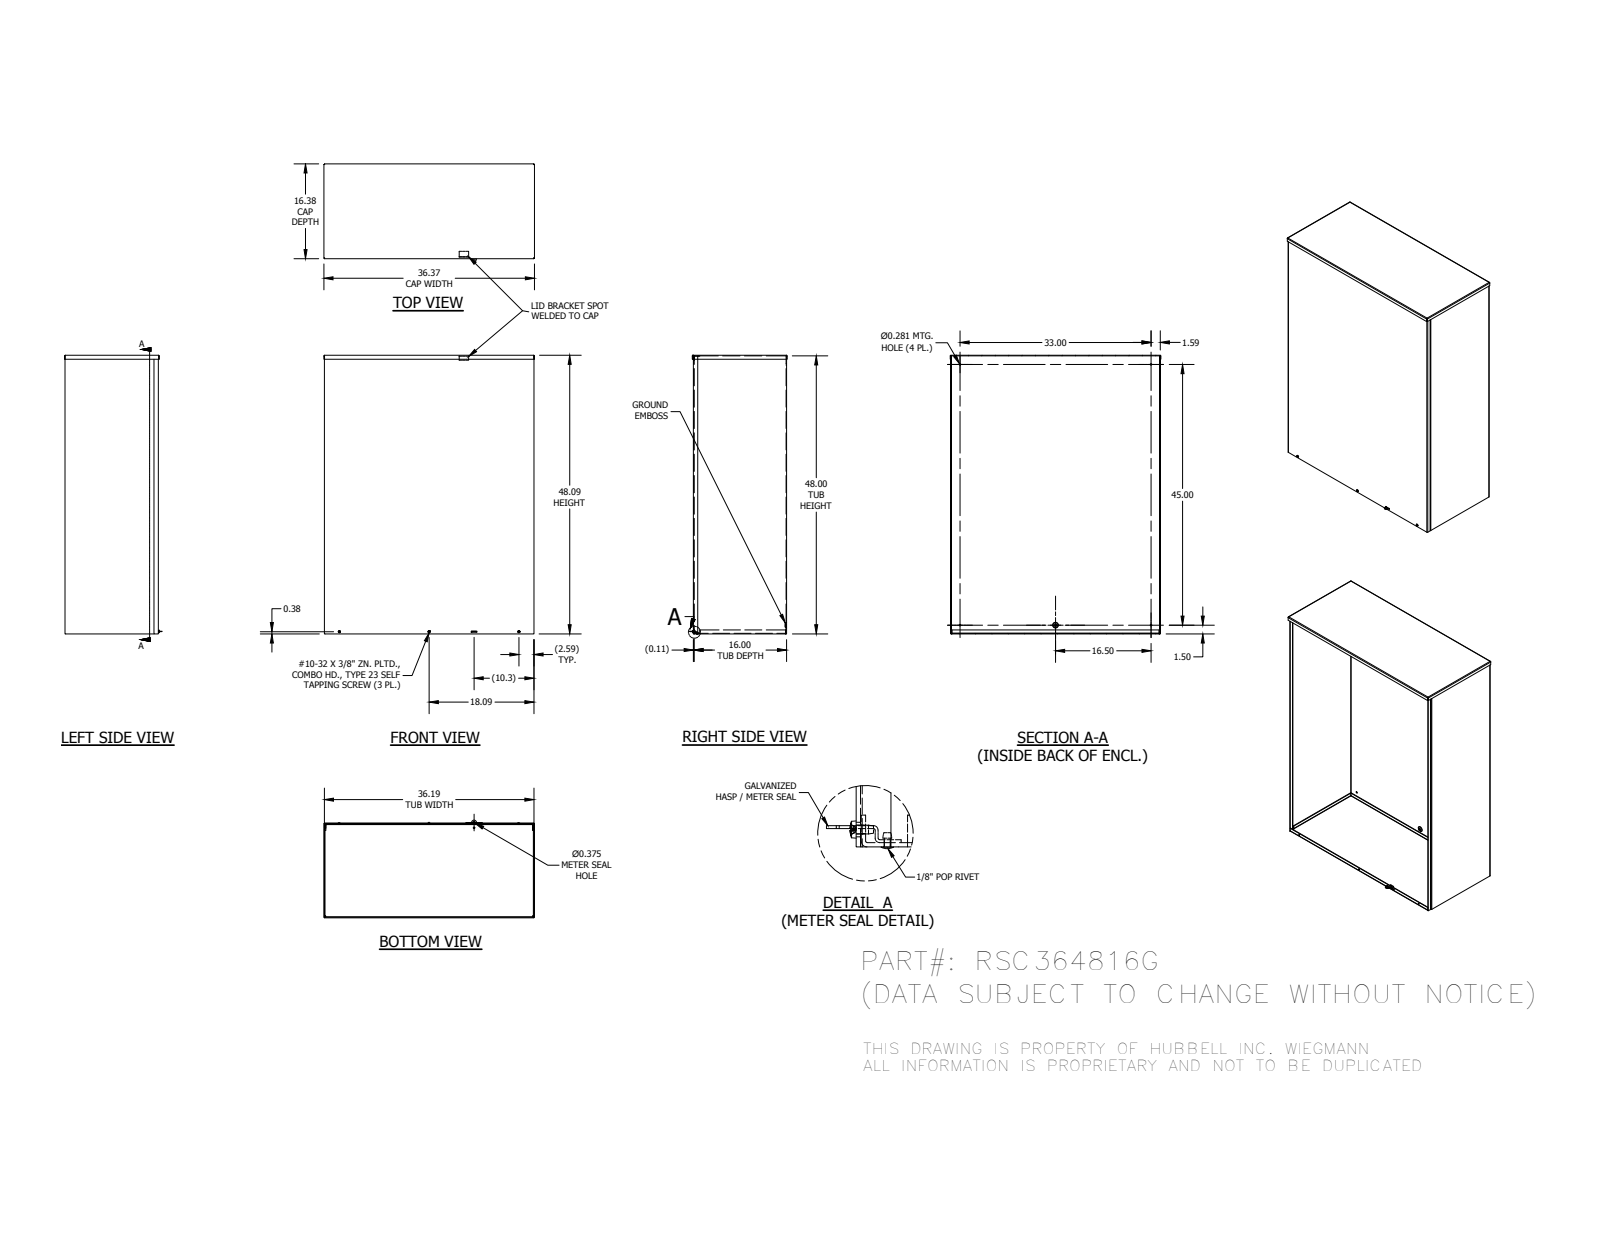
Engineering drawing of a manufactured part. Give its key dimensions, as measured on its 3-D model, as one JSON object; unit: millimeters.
{"part_name": "RSC364816GBKPA; RSC3616GEWPA; RSC3648GLFA; RSC3616GCPA (+5 more)", "step_written_by": "Autodesk Inventor 2014 (AUTOMOTIVE_DESIGN)", "units": "millimeters", "bodies": {"solids": 11, "faces": 367, "planar": 226, "cylindrical": 64, "other": 77}, "overall_size": [1222.6, 923.92, 427.84], "volume_mm3": 9748000, "surface_area_mm2": 8233000, "round_holes": [[7.94, 6], [4.34, 4], [7.14, 4], [3.17, 1], [3.45, 1], [9.52, 1]], "round_bosses_or_shafts": [[4.83, 3], [6.65, 1], [3.17, 1]], "partial_cylinders_radius": [[0.79, 19], [3.17, 16], [2.37, 2], [2.67, 1], [10.16, 1]], "face_to_face_distances": [2.38, 406.8, 409.18, 404.42, 916.78, 1219.2, 919.16, 914.4, 1221.58, 1216.82], "hole_center_spacings": [393.7, 813.3, 1263.08, 420.07, 1244.28, 38.24, 394.74, 787.4]}
